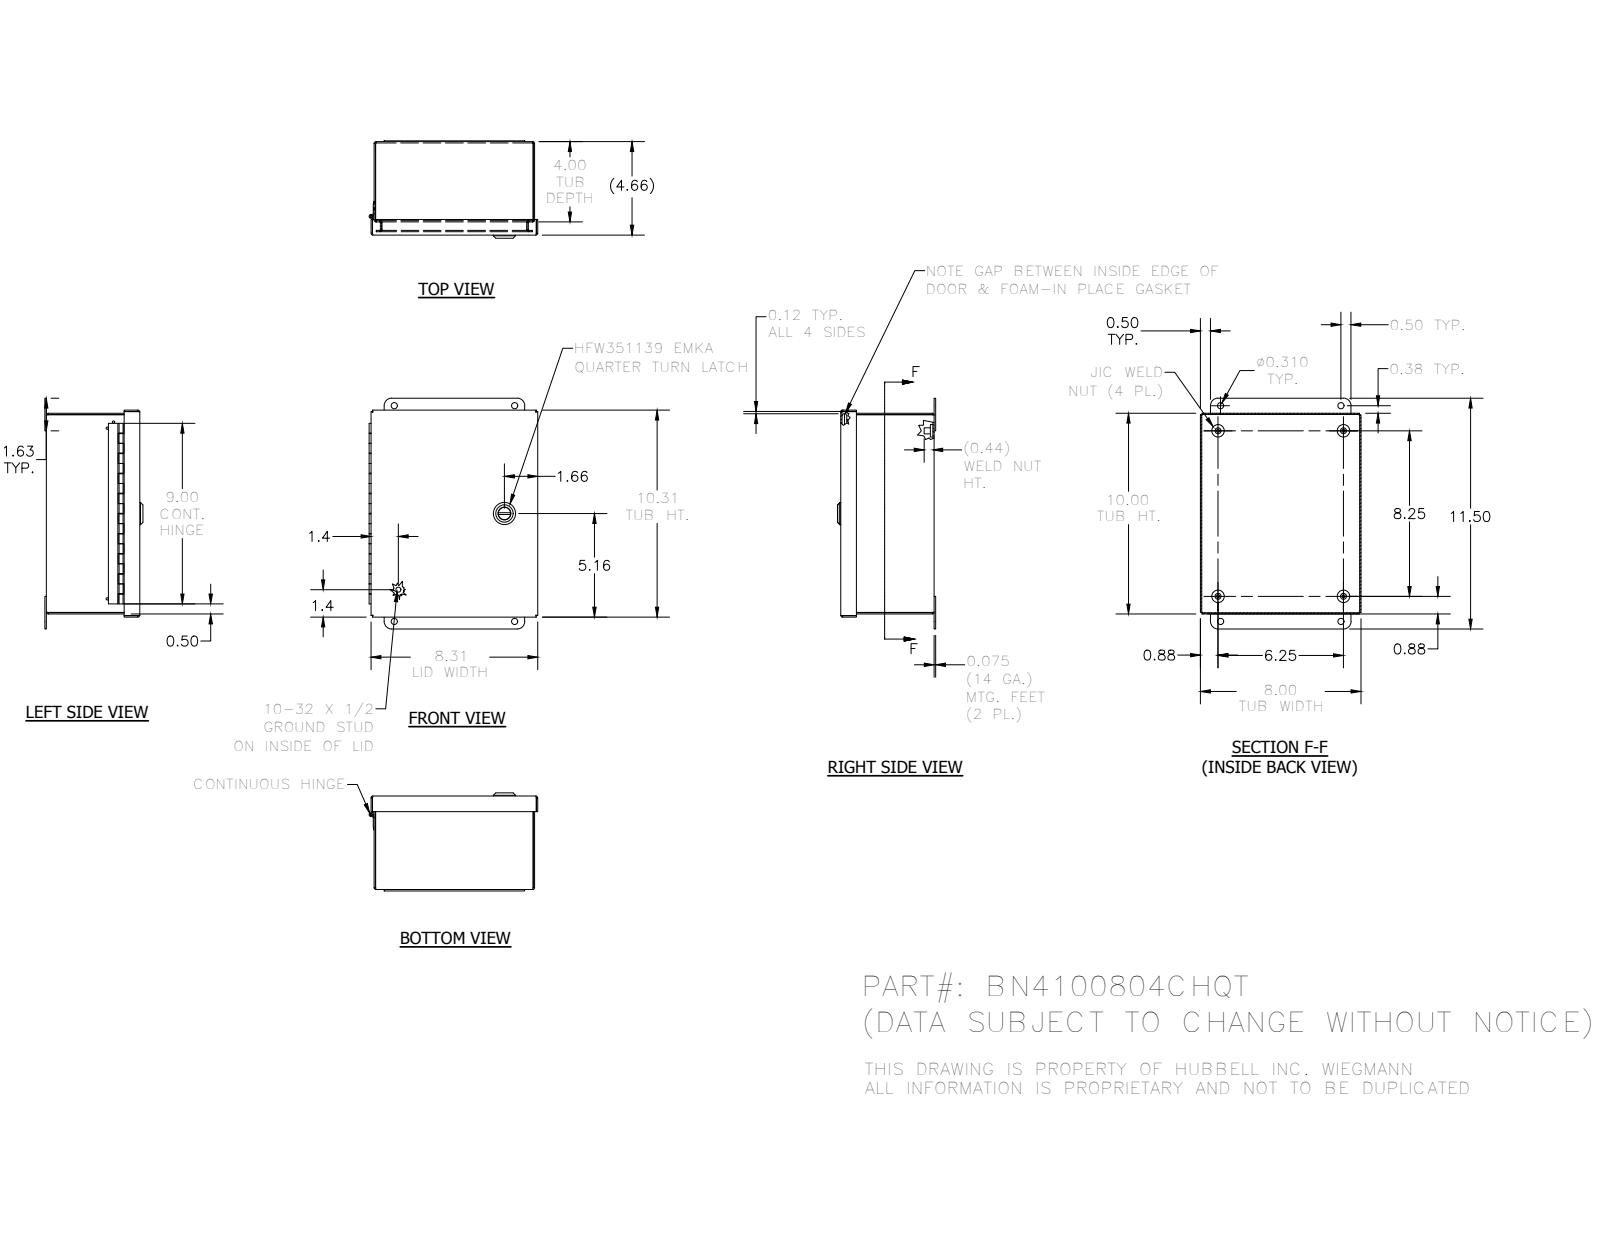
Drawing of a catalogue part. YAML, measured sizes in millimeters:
part_name: "BN4100804CHQT_a"
step_written_by: "SolidWorks 2018 (AUTOMOTIVE_DESIGN)"
units: millimeters
bodies: {solids: 21, faces: 765, planar: 384, cylindrical: 253, other: 128}
overall_size: [292.1, 213.5, 124.2]
volume: 476400
surface_area: 565000
round_holes:
  - {diameter: 4, count: 4}
  - {diameter: 7.9, count: 4}
  - {diameter: 3, count: 3}
  - {diameter: 2.9, count: 1}
  - {diameter: 5, count: 1}
  - {diameter: 8, count: 1}
  - {diameter: 10, count: 1}
  - {diameter: 10.2, count: 1}
  - {diameter: 16.1, count: 1}
  - {diameter: 20.4, count: 1}
round_bosses_or_shafts:
  - {diameter: 15.9, count: 4}
  - {diameter: 7.6, count: 4}
  - {diameter: 28, count: 1}
  - {diameter: 22, count: 1}
  - {diameter: 19.8, count: 1}
  - {diameter: 15.8, count: 1}
  - {diameter: 15.2, count: 1}
  - {diameter: 13.5, count: 1}
partial_cylinders:
  - {radius: 0.3, count: 30}
  - {radius: 0.8, count: 20}
  - {radius: 2.4, count: 20}
  - {radius: 3.2, count: 16}
  - {radius: 0.5, count: 12}
  - {radius: 4, count: 4}
  - {radius: 9.5, count: 4}
  - {radius: 0.4, count: 2}
face_to_face_distances: [1.6, 1.6, 116.7, 118.3, 115.1, 116.7, 252.4, 201.6, 200.1, 203.2]
hole_center_spacings: [287.1, 31.9, 152.4, 158.8, 158.8, 209.6, 241.3, 273.1]
